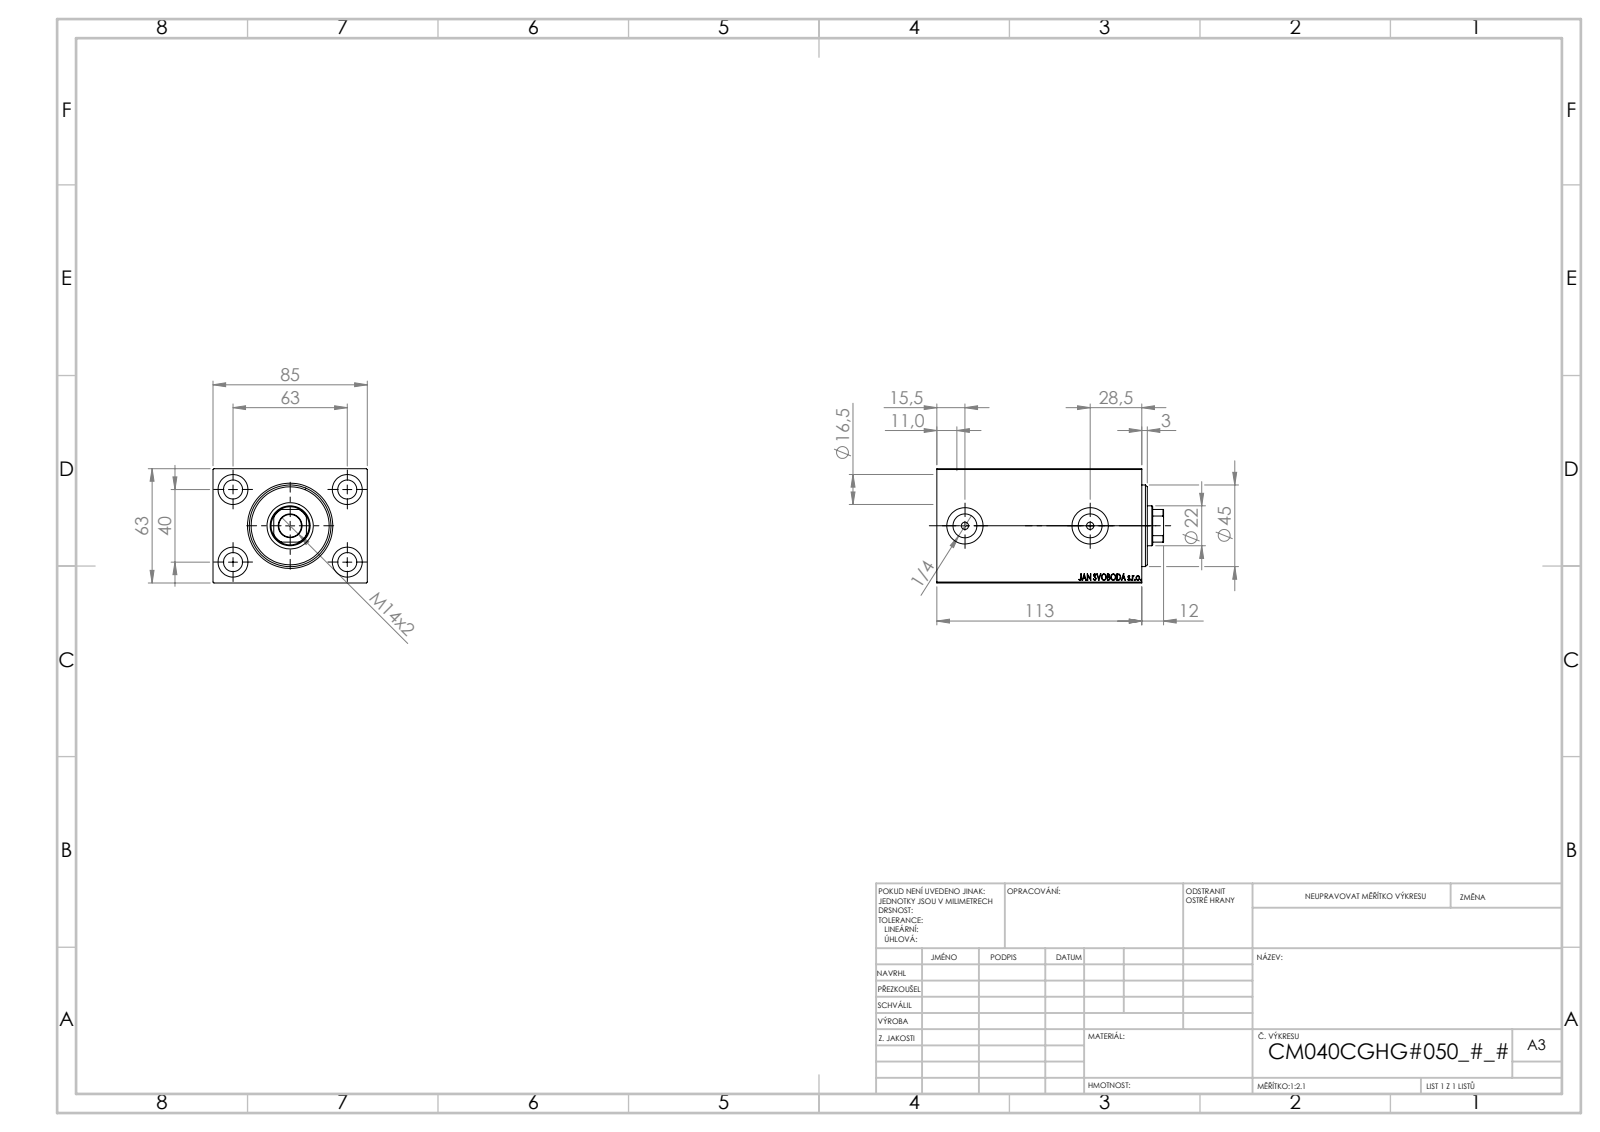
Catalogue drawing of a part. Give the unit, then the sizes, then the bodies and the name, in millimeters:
Units: millimetres
Overall size (bounding box): 125 × 85 × 63
Round holes (diameter × count): ⌀10.5 ×4, ⌀16.5 ×4, ⌀4 ×2, ⌀13.16 ×2, ⌀20 ×2, ⌀12.5 ×1, ⌀22 ×1, ⌀25.5 ×1, ⌀40 ×1, ⌀42 ×1, ⌀45 ×1
Partial cylindrical surfaces — rounded edges, fillets, slot ends (radius × count): R10.5 ×1
Main face-to-face distances: 63, 85, 113, 12, 101, 28.6, 72.4, 84.4, 11, 102
Hole centre spacings: 37.31, 40, 63, 74.63, 69
Volume: 511 963 mm³ · Surface area: 95 223 mm²
Bodies: 3 solids, 862 faces (408 planar, 60 cylindrical, 394 other)
Part name (STEP PRODUCT): V450CM_VC_B; V450CM_C_VCP; V450CM_C_Body
STEP written by: SolidWorks 2019 (CONFIG_CONTROL_DESIGN)
